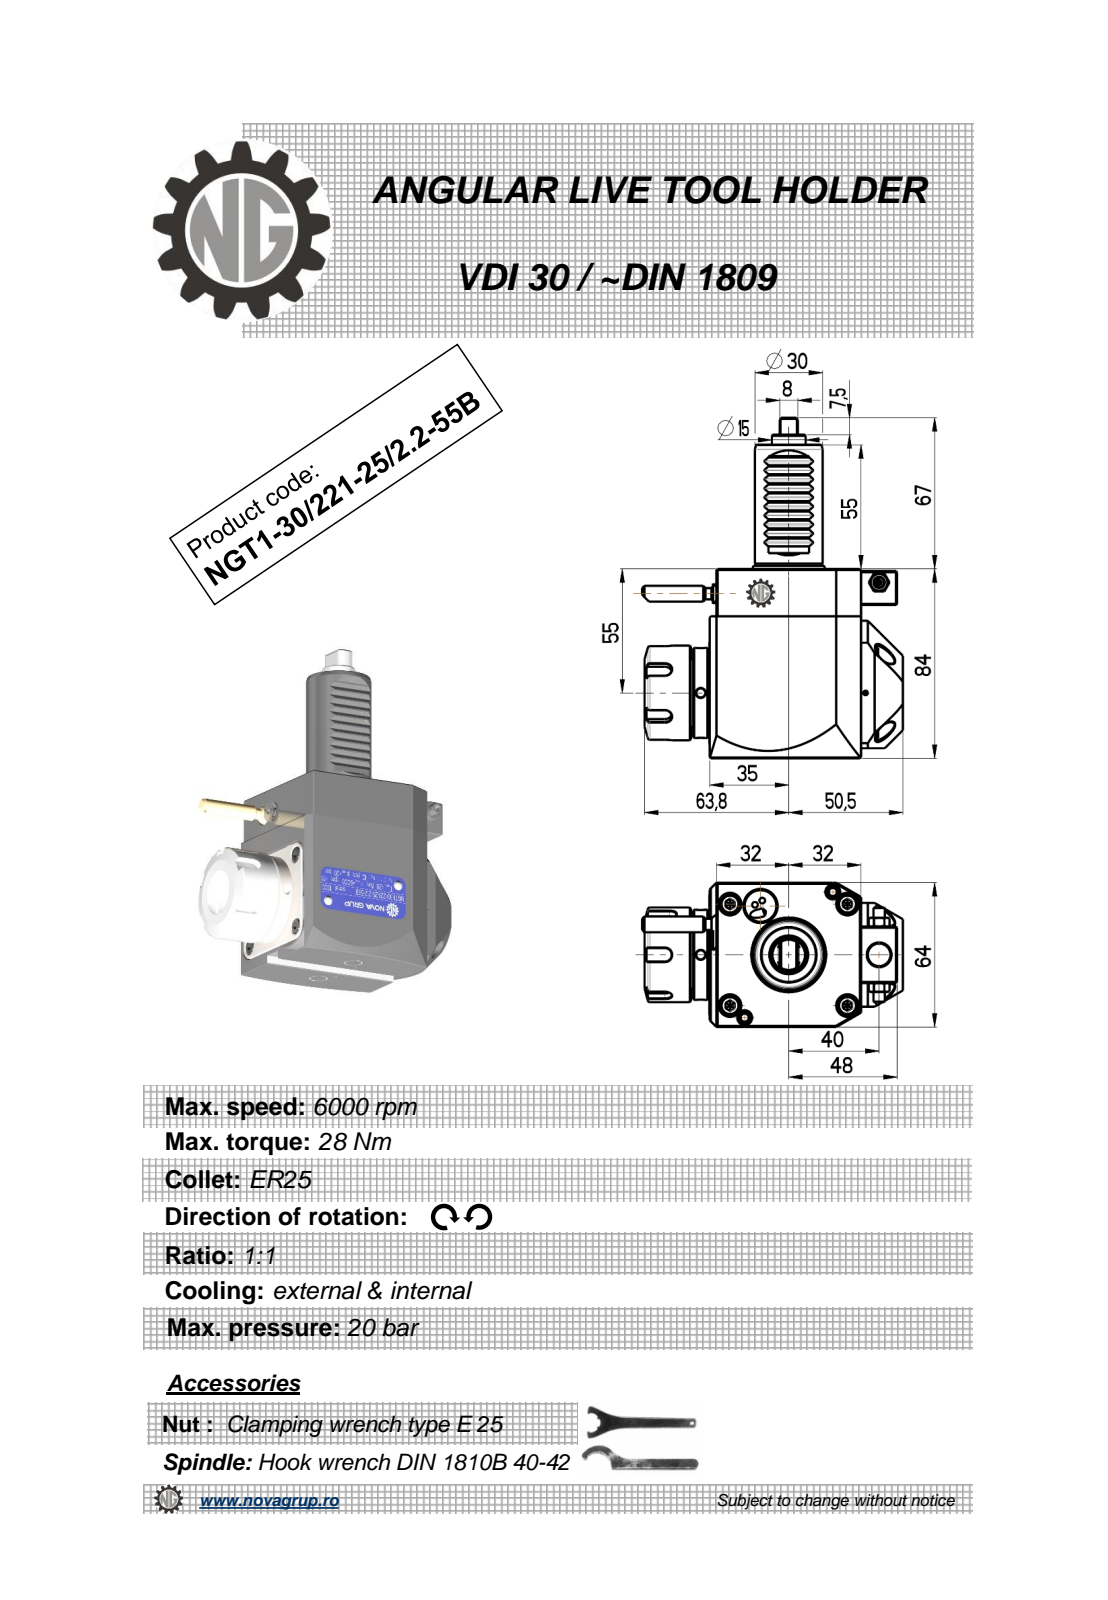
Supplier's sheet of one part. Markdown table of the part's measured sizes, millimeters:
| quantity | value |
| --- | --- |
| part name | NGT1_30_221_25_2_2_55B |
| STEP written by | PRO/ENGINEER BY PARAMETRIC TECHNOLOGY CORPORATION, 2010280 (CONFIG_CONTROL_DESIGN) |
| units | millimeters |
| bodies | 1 solid, 484 faces (196 planar, 116 cylindrical, 172 other) |
| overall size | 151 × 115.38 × 64 |
| volume | 457 191 mm³ |
| surface area | 48 368 mm² |
| round holes (diameter × count) | 3.3 × 4, 4.5 × 4, 8 × 4, 4 × 2, 2.5 × 1, 3 × 1, 4.2 × 1, 9.5 × 1, 10 × 1, 20.3 × 1, 42 × 1 |
| round bosses / shafts (diameter × count) | 8.96 × 2, 5 × 2, 41.8 × 1, 40 × 1, 33 × 1, 30 × 1, 15 × 1, 7 × 1 |
| partial cylindrical surfaces (radius × count) | 0.26 × 12, 0.3 × 10, 3 × 5, 0.8 × 2, 160 × 2, 7.2 × 1, 32 × 1 |
| main face-to-face distances | 64, 84, 67.2, 67, 3.2, 3, 80, 55, 85.7, 85.5 |
| hole center spacings | 24, 33.94, 34.06, 48, 65.7, 13.73, 27.25, 40.73 |
